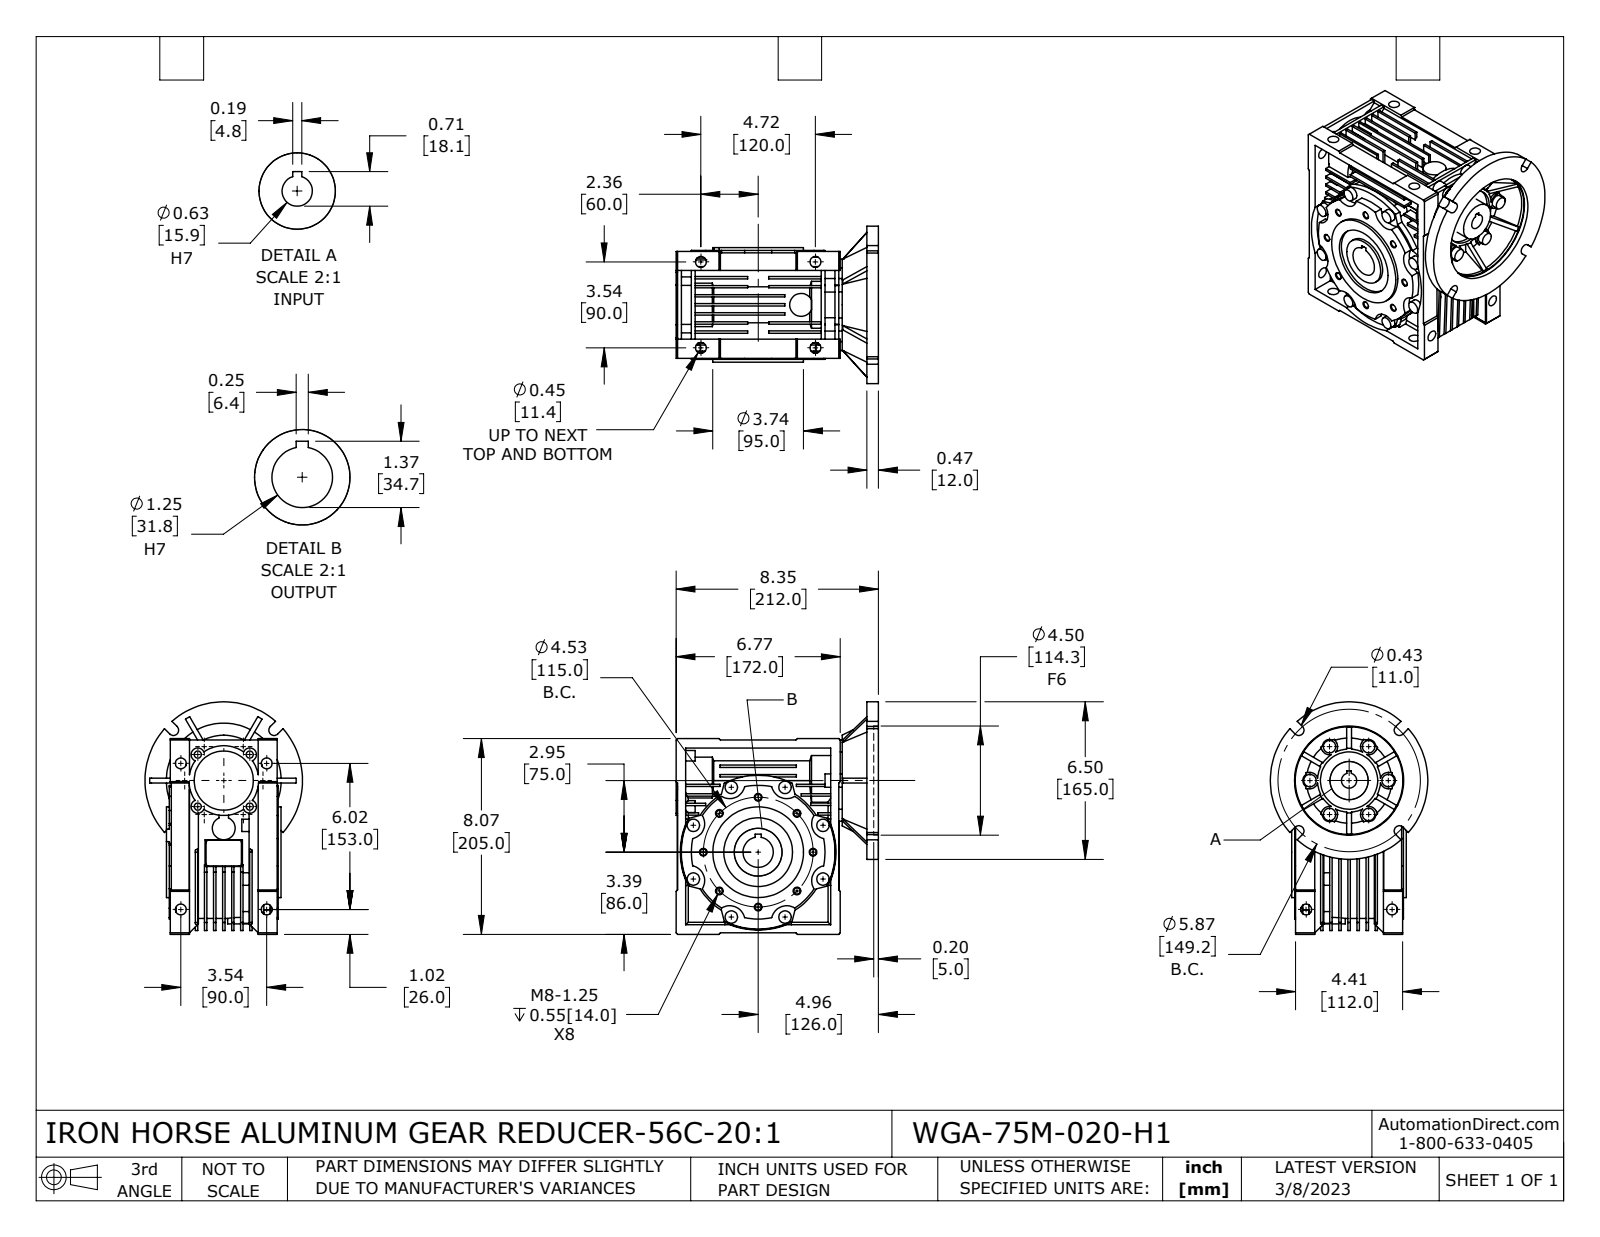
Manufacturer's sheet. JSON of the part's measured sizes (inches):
{"part_name": "WGA-75M-020-H1", "step_written_by": "SolidWorks 2021 (CONFIG_CONTROL_DESIGN)", "units": "inches", "bodies": {"solids": 4, "faces": 1179, "planar": 675, "cylindrical": 386, "other": 118}, "overall_size": [9.587, 8.346, 6.496], "volume_in3": 180.8, "surface_area_in2": 779.6, "round_holes": [[0.262, 8], [0.448, 8], [0.293, 4], [0.625, 1], [0.65, 1], [1, 1], [1.25, 1], [1.535, 1], [1.654, 1], [1.969, 1], [2.441, 1], [2.677, 1]], "round_bosses_or_shafts": [[0.512, 14], [0.945, 3], [6.496, 1], [5.509, 1], [5.465, 1], [3.74, 1], [2.992, 1], [2.795, 1]], "partial_cylinders_radius": [[0.276, 10], [0.63, 8], [0.295, 6], [0.335, 6], [0.098, 4], [0.217, 4], [1.299, 1], [1.417, 1]], "face_to_face_distances": [0.374, 0.098, 0.472, 0.748, 0.276, 1.122, 1.496, 0.394, 0.65, 0.846], "hole_center_spacings": [2.264, 1.733, 3.202, 4.183, 1.515, 2.143, 3.543, 4.528]}
